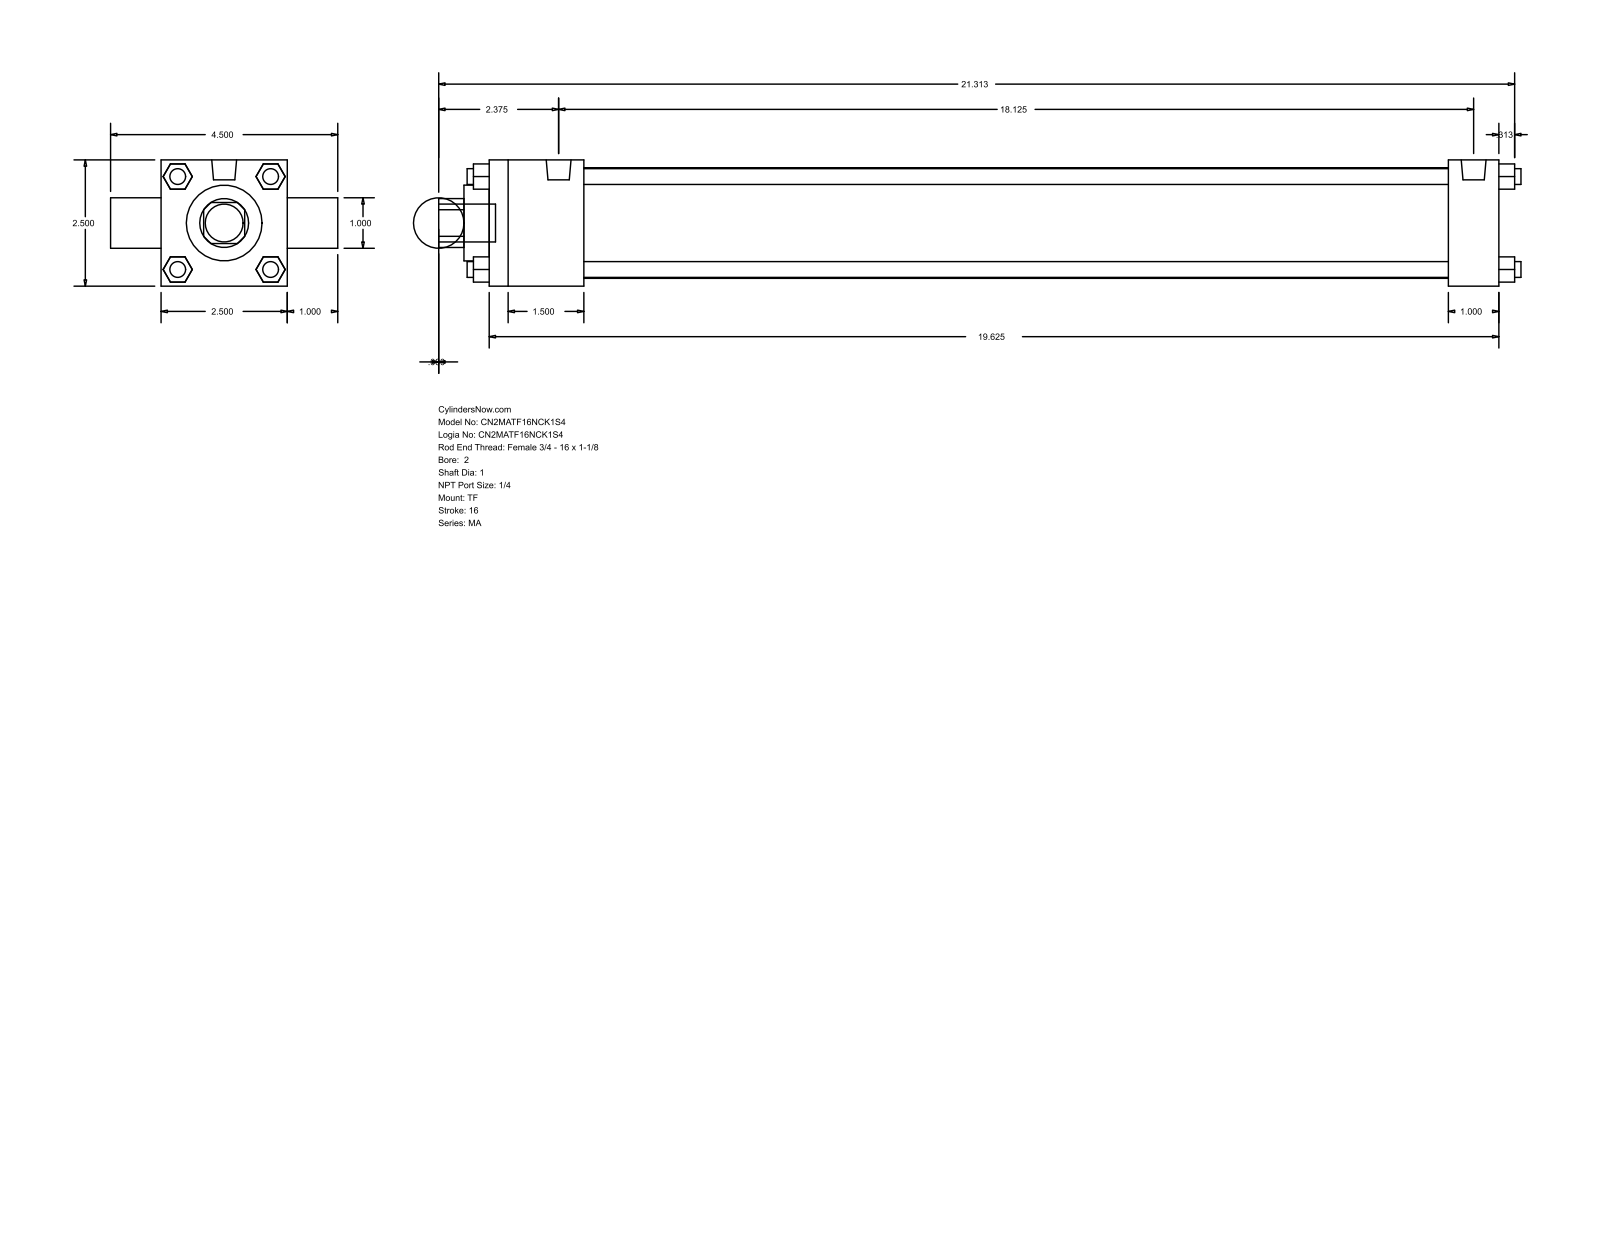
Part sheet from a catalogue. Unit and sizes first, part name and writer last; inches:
Units: inches
Overall size (bounding box): 21.437 × 4.5 × 2.5
Round holes (diameter × count): ⌀1 ×2, ⌀1.5 ×1, ⌀2.19 ×1
Round bosses / shafts (diameter × count): ⌀0.313 ×7, ⌀0.492 ×2, ⌀0.75 ×1
Partial cylindrical surfaces — rounded edges, fillets, slot ends (radius × count): R0.484 ×1
Main face-to-face distances: 2.5, 1, 20, 0.5, 1.875, 19, 17.125, 18.125, 3.5, 0.92
Bodies: 0 solids, 120 faces (92 planar, 28 cylindrical, 0 other)
Part name (STEP PRODUCT): MA_TF__0200_1
STEP written by: GSSL Pune (CONFIG_CONTROL_DESIGN)
